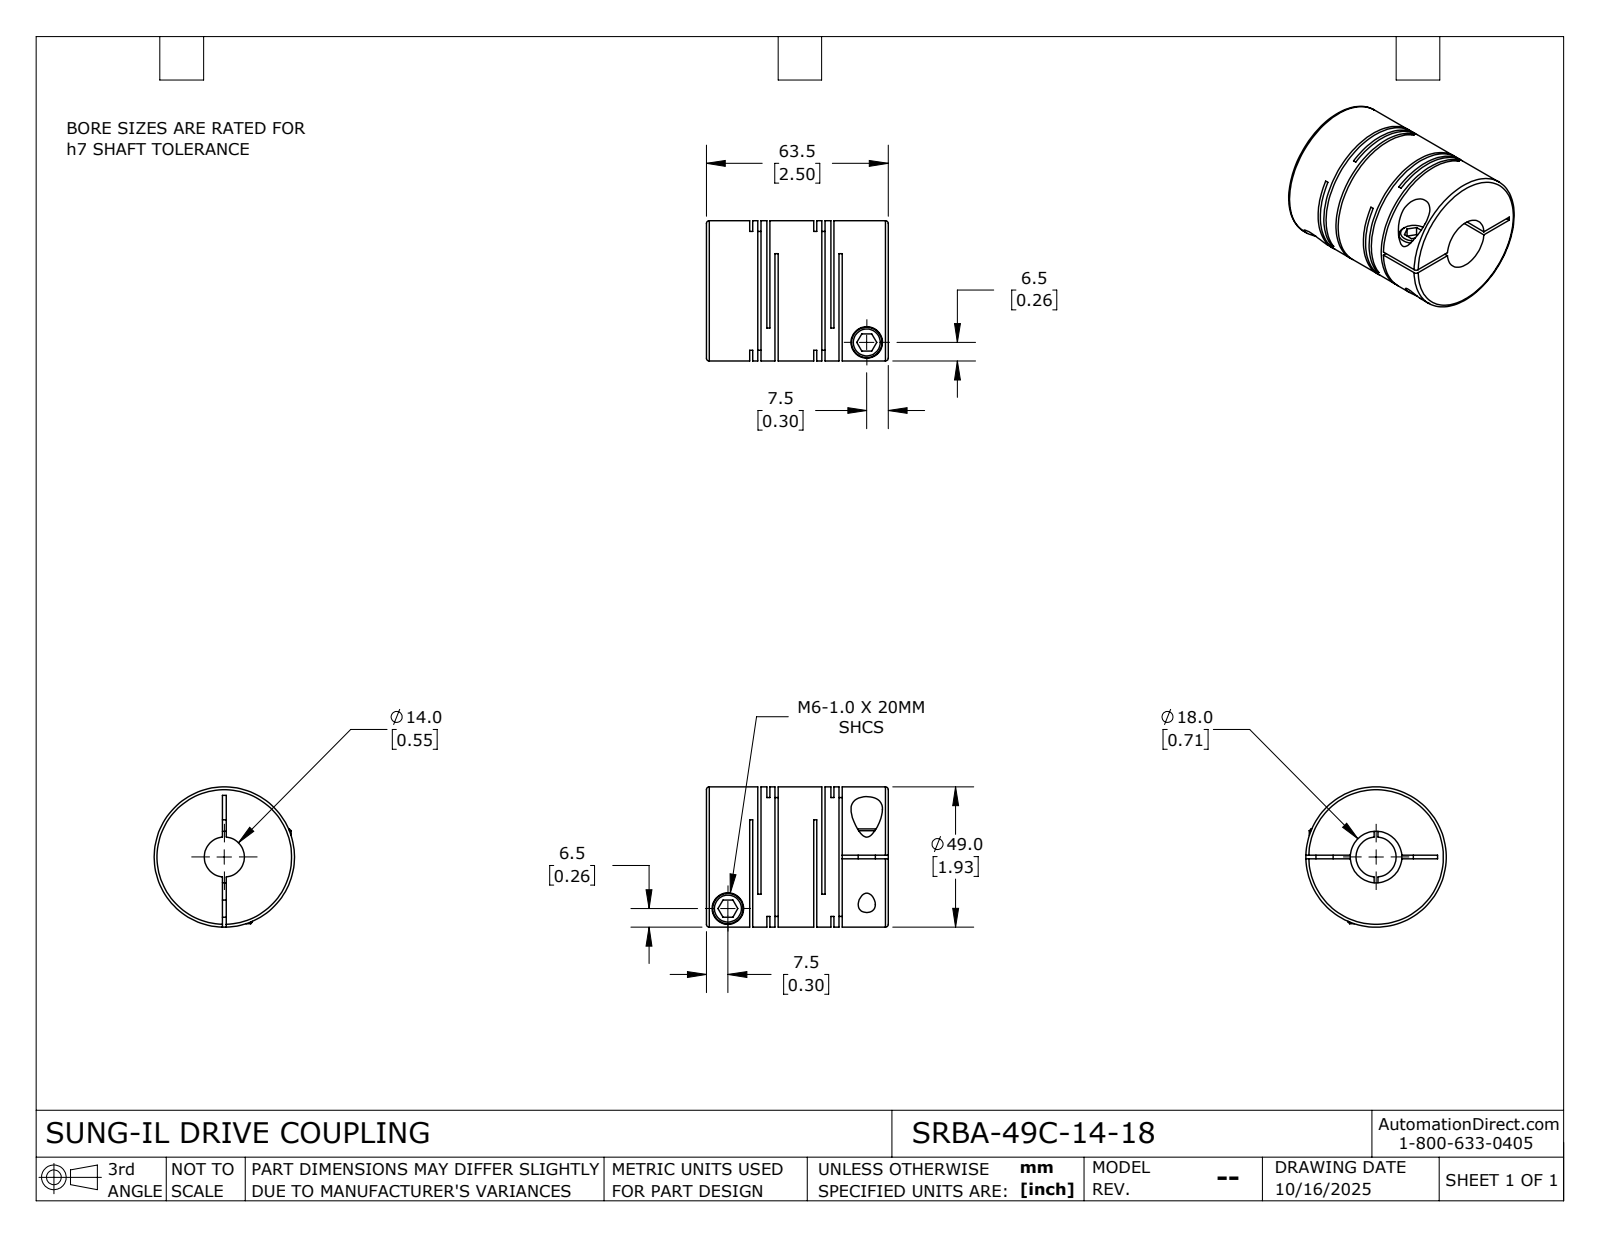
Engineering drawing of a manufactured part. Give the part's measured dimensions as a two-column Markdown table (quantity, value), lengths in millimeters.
| quantity | value |
| --- | --- |
| part name | SRBA-49C-14-18 |
| STEP written by | SolidWorks 2024 (CONFIG_CONTROL_DESIGN) |
| units | millimeters |
| bodies | 1 solid, 115 faces (60 planar, 42 cylindrical, 13 other) |
| overall size | 63.5 × 49 × 49 |
| volume | 90 833 mm³ |
| surface area | 38 942 mm² |
| round holes (diameter × count) | 6 × 2, 11 × 2, 14 × 1, 18 × 1 |
| round bosses / shafts (diameter × count) | 10.6 × 2, 49 × 1 |
| main face-to-face distances | 6, 1.1, 22.35, 2.85, 21.25, 3.15, 19.5, 16.35, 1.75, 4.9 |
